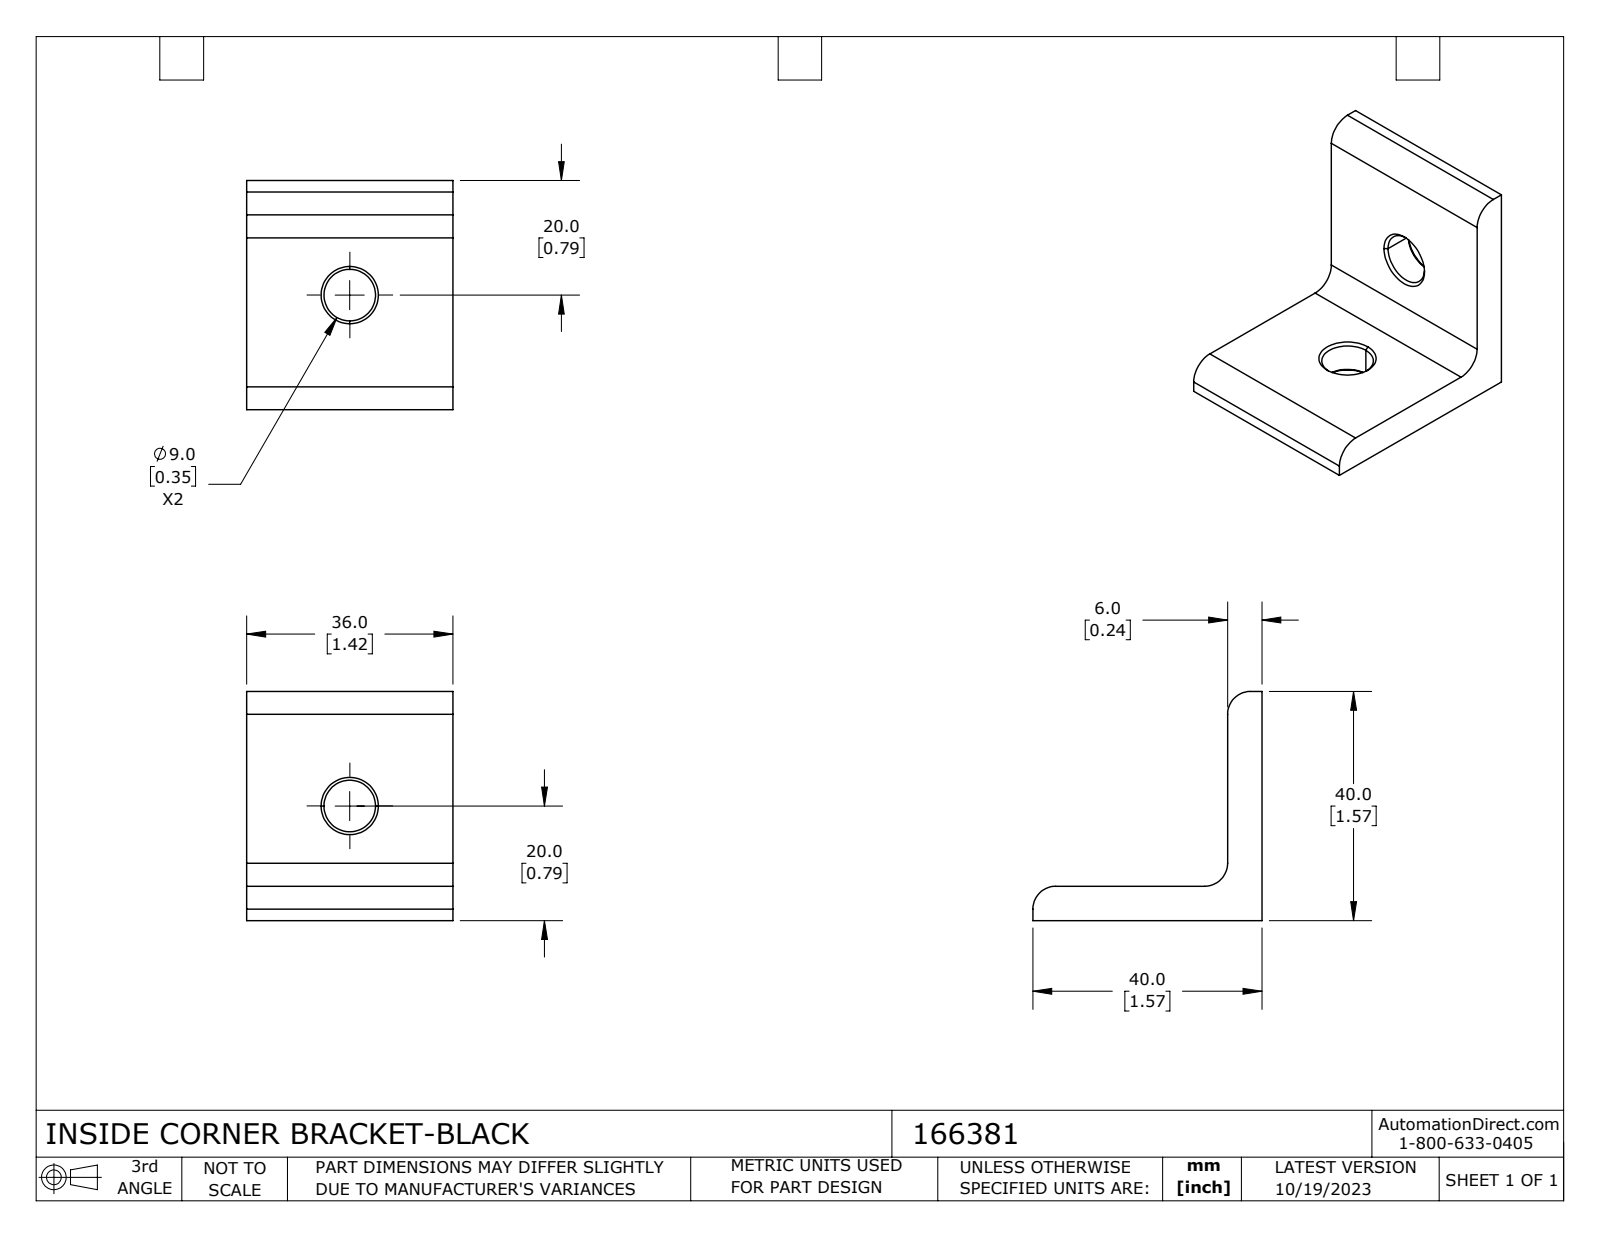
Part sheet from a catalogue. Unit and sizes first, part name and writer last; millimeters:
Units: millimetres
Overall size (bounding box): 40 × 40 × 36
Round holes (diameter × count): ⌀9 ×2
Partial cylindrical surfaces — rounded edges, fillets, slot ends (radius × count): R4 ×3
Main face-to-face distances: 6, 36, 40, 34
Volume: 15 082 mm³ · Surface area: 6 509 mm²
Bodies: 1 solid, 23 faces (8 planar, 7 cylindrical, 8 other)
Part name (STEP PRODUCT): 166381
STEP written by: SolidWorks 2023 (CONFIG_CONTROL_DESIGN)
